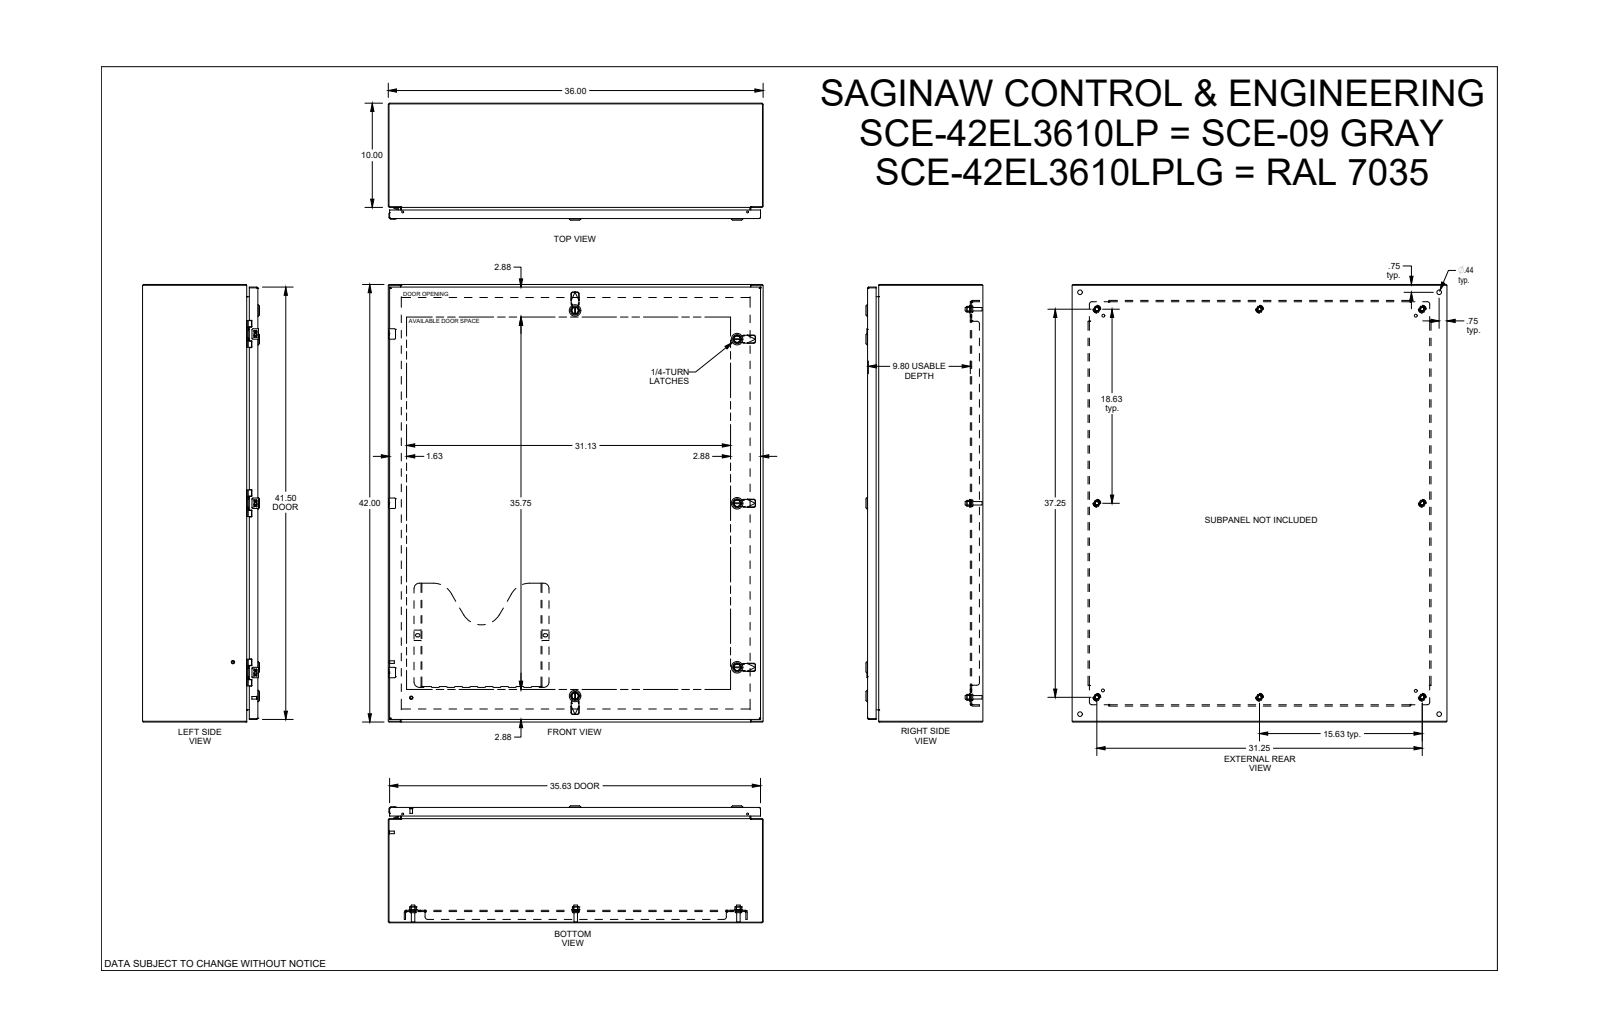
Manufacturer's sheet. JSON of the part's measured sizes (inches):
{"part_name": "SCE-42EL3610LP", "step_written_by": "SolidWorks 2019 (CONFIG_CONTROL_DESIGN)", "units": "inches", "bodies": {"solids": 0, "faces": 4774, "planar": 2327, "cylindrical": 1328, "other": 1119}, "overall_size": [42, 36, 11.23], "round_holes": [[0.367, 8], [0.5, 8], [0.172, 6], [0.205, 6], [0.244, 6], [0.266, 6], [0.375, 6], [0.197, 5], [0.315, 5], [0.394, 5], [0.634, 5], [0.281, 4]], "round_bosses_or_shafts": [[0.17, 9], [0.366, 8], [0.332, 8], [0.25, 6], [0.24, 6], [1.102, 5], [0.866, 5], [0.802, 5]], "partial_cylinders_radius": [[0.012, 136], [0.01, 52], [0.02, 52], [0.015, 32], [0.157, 20], [0.04, 17], [0.025, 16], [0.1, 16]], "face_to_face_distances": [0.075, 0.075, 10.923, 10.998, 11.073, 10.998, 1.2, 9.873, 1, 1.125], "hole_center_spacings": [16.25, 0.985, 32.5, 0.02, 0.493, 0.494, 4.493, 15.265]}
